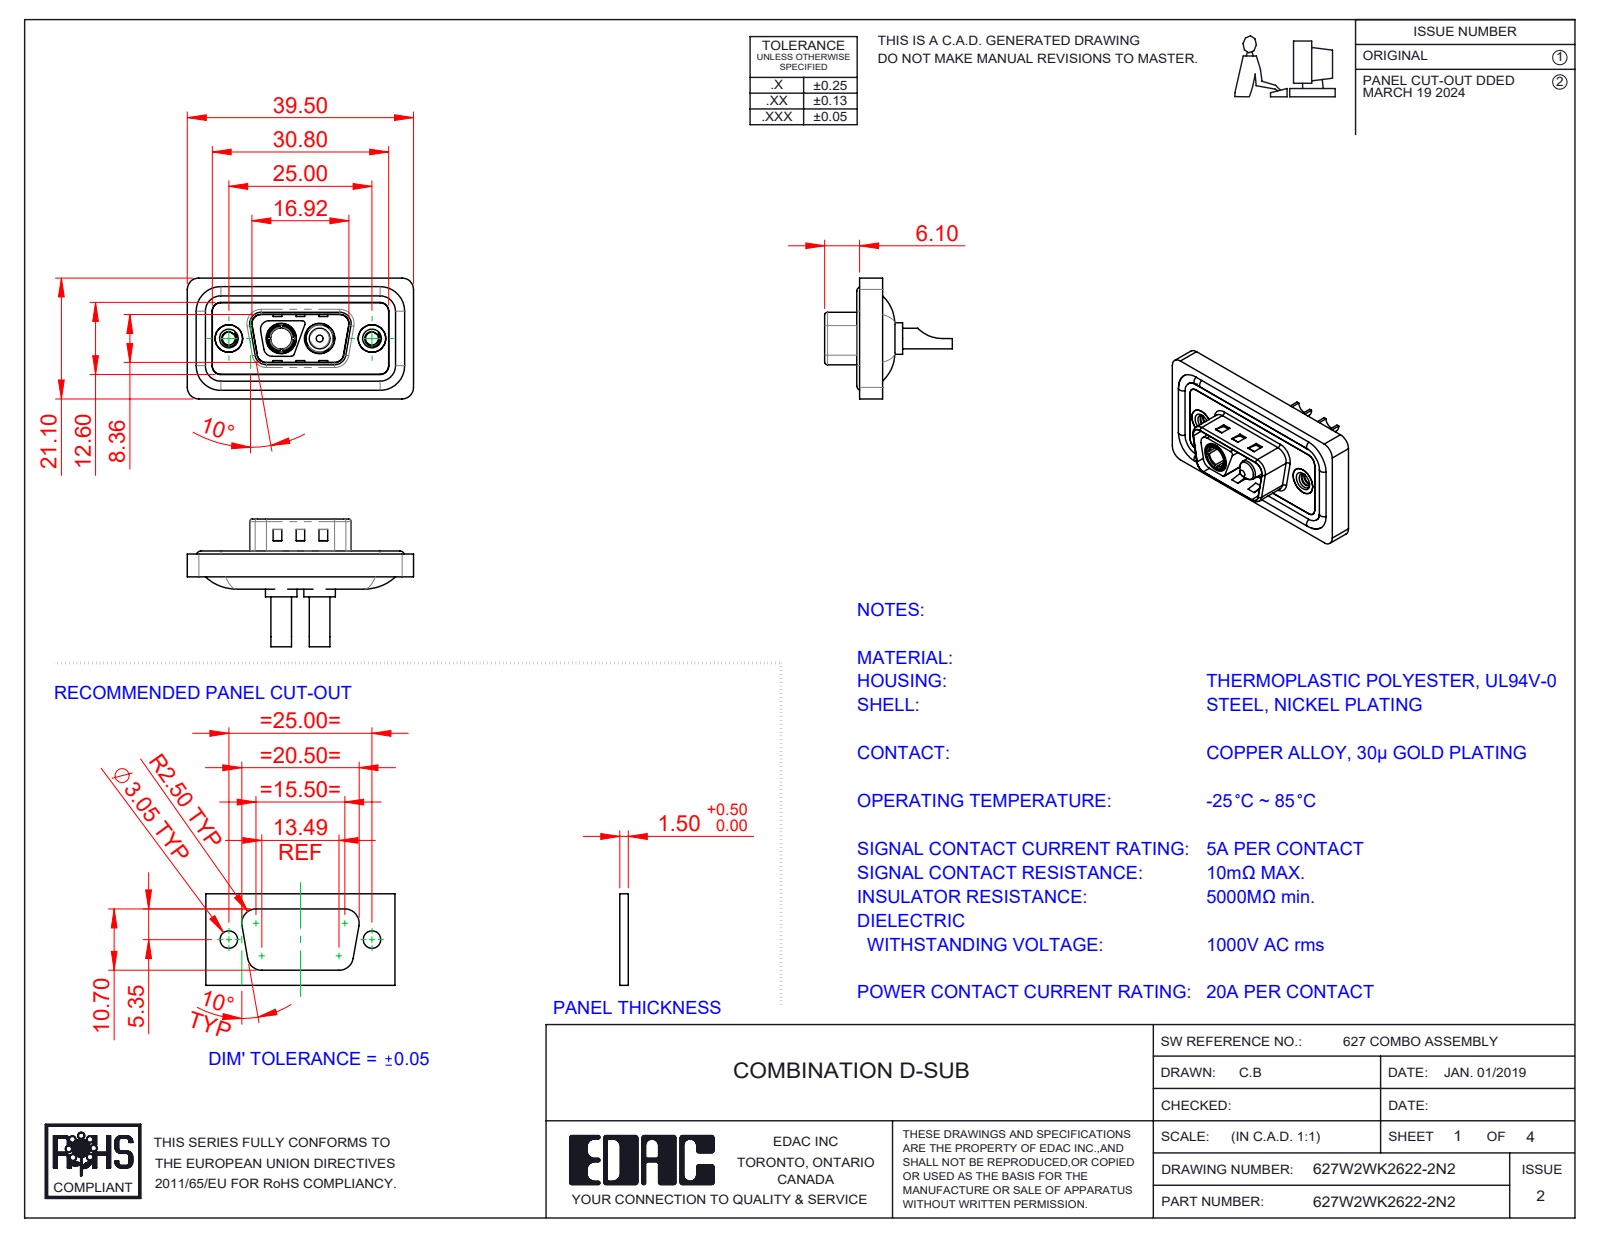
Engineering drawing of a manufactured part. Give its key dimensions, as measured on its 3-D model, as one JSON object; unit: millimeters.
{"part_name": "627Combo Housing_2WK2; Power Pin_20A SC; Power Socket_20A SC; 627Combo Waterproof Housing_09 Contacts (+4 more)", "step_written_by": "SolidWorks 2023 (CONFIG_CONTROL_DESIGN)", "units": "millimeters", "bodies": {"solids": 11, "faces": 548, "planar": 195, "cylindrical": 233, "other": 120}, "overall_size": [39.5, 22.3, 21.1], "volume_mm3": 4580, "surface_area_mm2": 7507, "round_holes": [[2.26, 2], [2.7, 2], [4, 2], [4.8, 2], [4.85, 2], [5, 2], [5.3, 2], [3.7, 1]], "round_bosses_or_shafts": [[1.6, 4], [5.5, 2], [5.2, 2], [4.9, 2], [4.75, 2], [3.75, 2], [3.6, 2], [4.96, 1]], "partial_cylinders_radius": [[1.5, 24], [2, 18], [0.5, 10], [1.6, 8], [0.25, 4], [0.6, 4], [0.65, 4], [0.9, 4]], "face_to_face_distances": [0.4, 1.1, 2.9, 0.5, 3.1, 1.6, 1.5, 4, 2.5, 1.8], "hole_center_spacings": [9.14, 15.86, 6.72, 25]}
